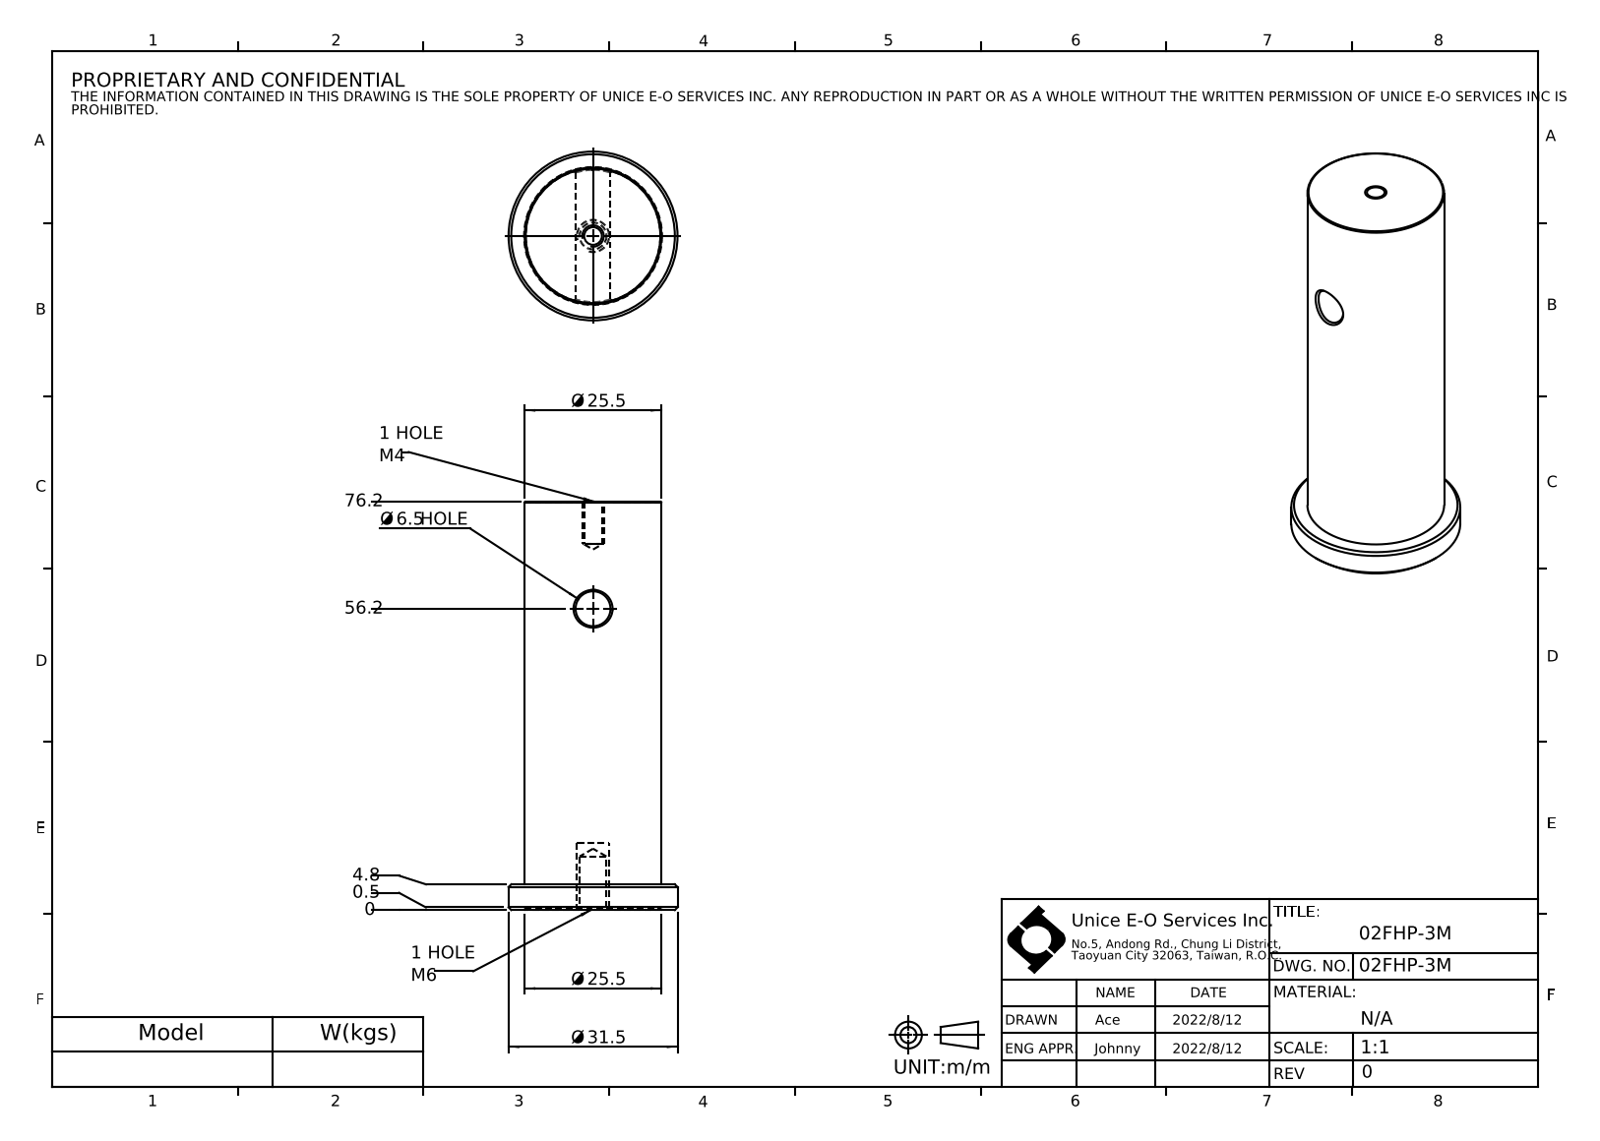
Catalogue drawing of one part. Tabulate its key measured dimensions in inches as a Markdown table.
| quantity | value |
| --- | --- |
| part name | 02FHP-3M |
| STEP written by | SolidWorks 2021 (CONFIG_CONTROL_DESIGN) |
| units | inches |
| bodies | 1 solid, 34 faces (4 planar, 12 cylindrical, 18 other) |
| overall size | 3 × 1.24 × 1.24 |
| volume | 2.369 in³ |
| surface area | 13 in² |
| round holes (diameter × count) | 0.13 × 1, 0.197 × 1, 0.256 × 1, 1.004 × 1 |
| round bosses / shafts (diameter × count) | 1.24 × 1 |
| main face-to-face distances | 2.98, 0.169, 2.811, 0.02, 0.189, 3 |
